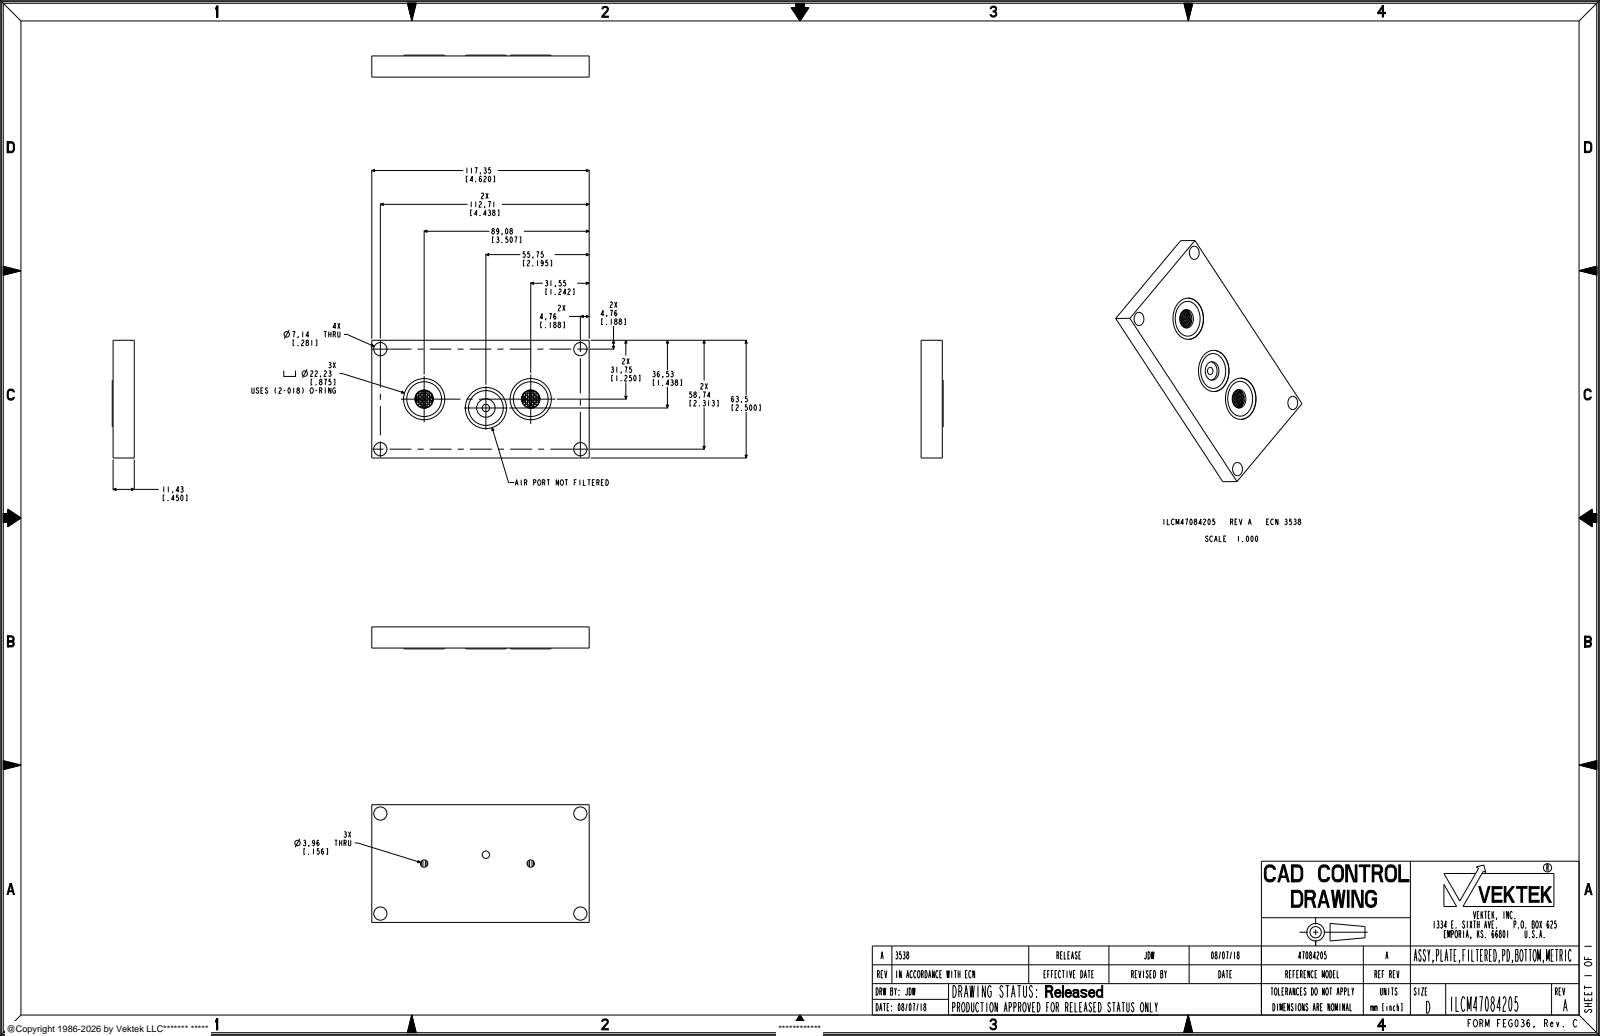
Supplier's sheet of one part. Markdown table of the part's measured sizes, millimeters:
| quantity | value |
| --- | --- |
| part name | ILCM47084205 |
| STEP written by | PRO/ENGINEER BY PARAMETRIC TECHNOLOGY CORPORATION, 2013320 (AUTOMOTIVE_DESIGN) |
| units | millimeters |
| bodies | 1 solid, 488 faces (168 planar, 310 cylindrical, 10 other) |
| overall size | 117.3 × 63.5 × 11.9 |
| volume | 80 920 mm³ |
| surface area | 22 720 mm² |
| round holes (diameter × count) | 1.6 × 32, 7.1 × 4, 4 × 3, 10 × 3, 22.2 × 3, 6.7 × 2, 7.4 × 2, 10.4 × 2 |
| round bosses / shafts (diameter × count) | 9.5 × 2, 9.4 × 2 |
| partial cylindrical surfaces (radius × count) | 0.8 × 32, 0.5 × 14, 0.4 × 8, 0.7 × 6, 0.3 × 4, 0.4 × 4, 0.6 × 4, 3.8 × 2 |
| main face-to-face distances | 11.4, 63.5, 10.1, 1.3, 117.3, 1.2, 2.5, 3.3, 0.8, 7.1 |
| hole center spacings | 1.7, 3.8, 5.3, 2.7, 2.4, 3.4, 3.8, 5.1 |
